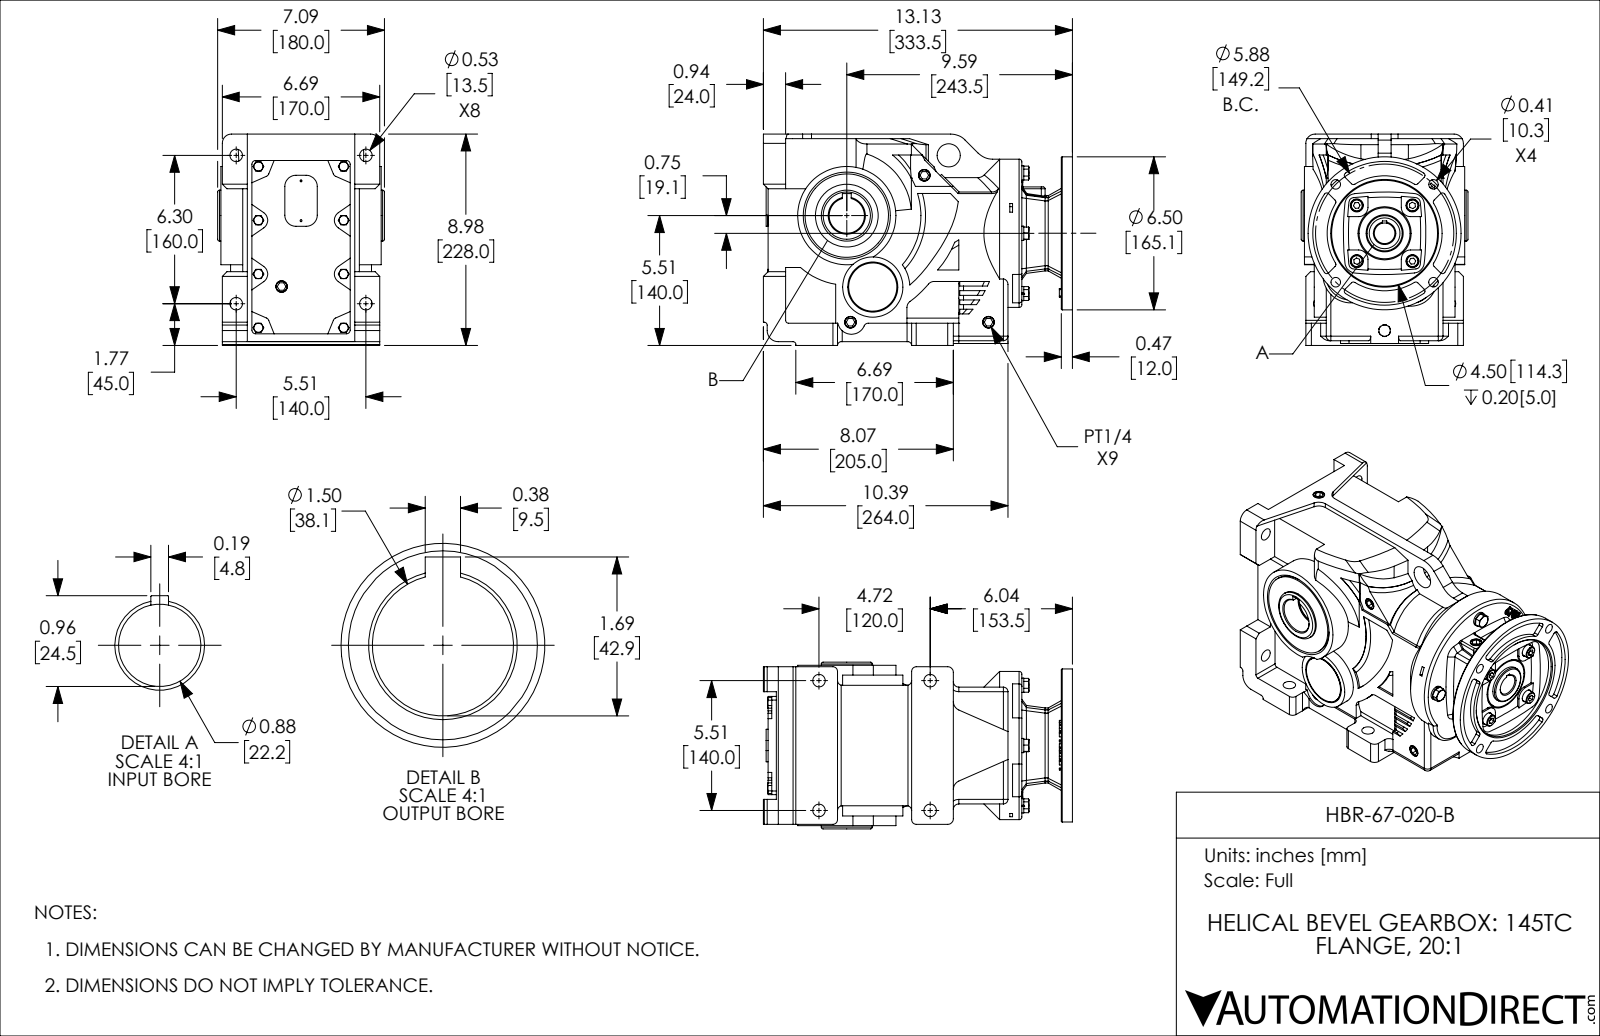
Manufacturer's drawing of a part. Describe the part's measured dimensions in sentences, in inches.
The part is named "HBR-67-020-B". Its 3-D file was written by "SolidWorks 2018 (AUTOMOTIVE_DESIGN)". It is 1 solid with 1131 faces: 598 planar, 268 cylindrical and 265 other. Overall it measures 13.13 by 8.976 by 7.087 inches. Its volume is 482.9 cubic inches and its surface area 639 square inches. Round holes: 8 of diameter 0.531, 4 of diameter 0.323, 4 of diameter 0.354, 4 of diameter 0.406, 4 of diameter 0.551, 2 of diameter 0.079, 1 of diameter 0.875, 1 of diameter 0.984, 1 of diameter 1.102, 1 of diameter 1.5, 1 of diameter 1.575, 1 of diameter 4.5. Round bosses or shafts: 4 of diameter 0.606, 4 of diameter 0.512, 4 of diameter 0.315, 2 of diameter 2.165, 1 of diameter 6.5, 1 of diameter 6.299, 1 of diameter 4.173, 1 of diameter 3.543. Partial cylindrical surfaces (rounded edges, fillets, slot ends): 20 of radius 0.197, 19 of radius 0.118, 15 of radius 0.394, 12 of radius 0.157, 7 of radius 0.079, 5 of radius 0.472, 4 of radius 0.236, 4 of radius 11.811. The main face-to-face distances are 0.197, 0.079, 0.945, 0.276, 0.059, 8.78, 4.961, 0.157, 0.118, 1.949. The hole center spacings are 2.132, 3.925, 1.264, 1.673, 1.815, 2.559, 2.937, 3.38.
